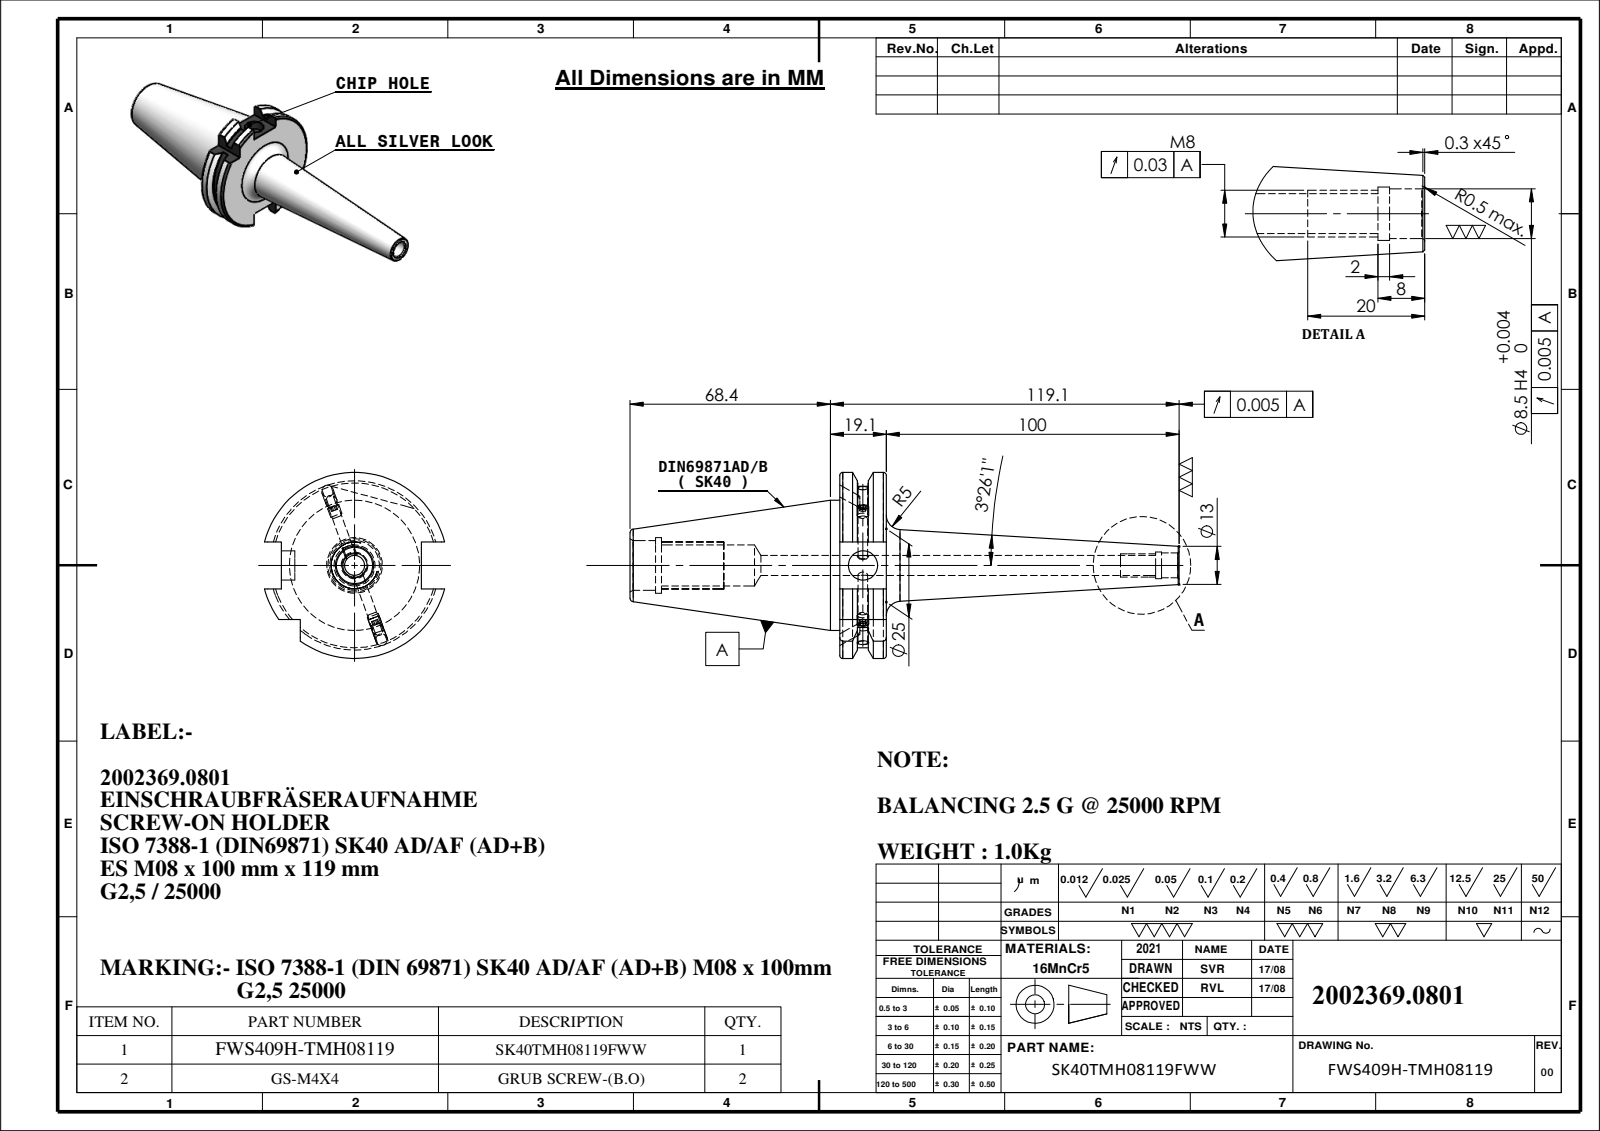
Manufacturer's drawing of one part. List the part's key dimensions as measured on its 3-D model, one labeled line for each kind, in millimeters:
Part name (STEP PRODUCT): 91406-ES7M08100; SK40TMH08119FWW; Copy of M4X4; Copy of M4X4_DIN 913 - M4 x 4-N
STEP written by: SolidWorks 2018 (CONFIG_CONTROL_DESIGN)
Units: millimetres
Bodies: 3 solids, 128 faces (48 planar, 36 cylindrical, 44 other)
Overall size (bounding box): 187.5 × 63.55 × 61.48
Volume: 129 377 mm³ · Surface area: 28 357 mm²
Round holes (diameter × count): ⌀3.3 ×1, ⌀6.8 ×1, ⌀8.5 ×1, ⌀9.1 ×1, ⌀10 ×1, ⌀14 ×1, ⌀17 ×1, ⌀19 ×1
Round bosses / shafts (diameter × count): ⌀4 ×2, ⌀44.45 ×1
Partial cylindrical surfaces — rounded edges, fillets, slot ends (radius × count): R28.12 ×1, R31.77 ×1
Main face-to-face distances: 15.9, 16.1, 47.8, 71.6, 87.5, 10.7, 60.9, 76.8, 77.62, 66.92
